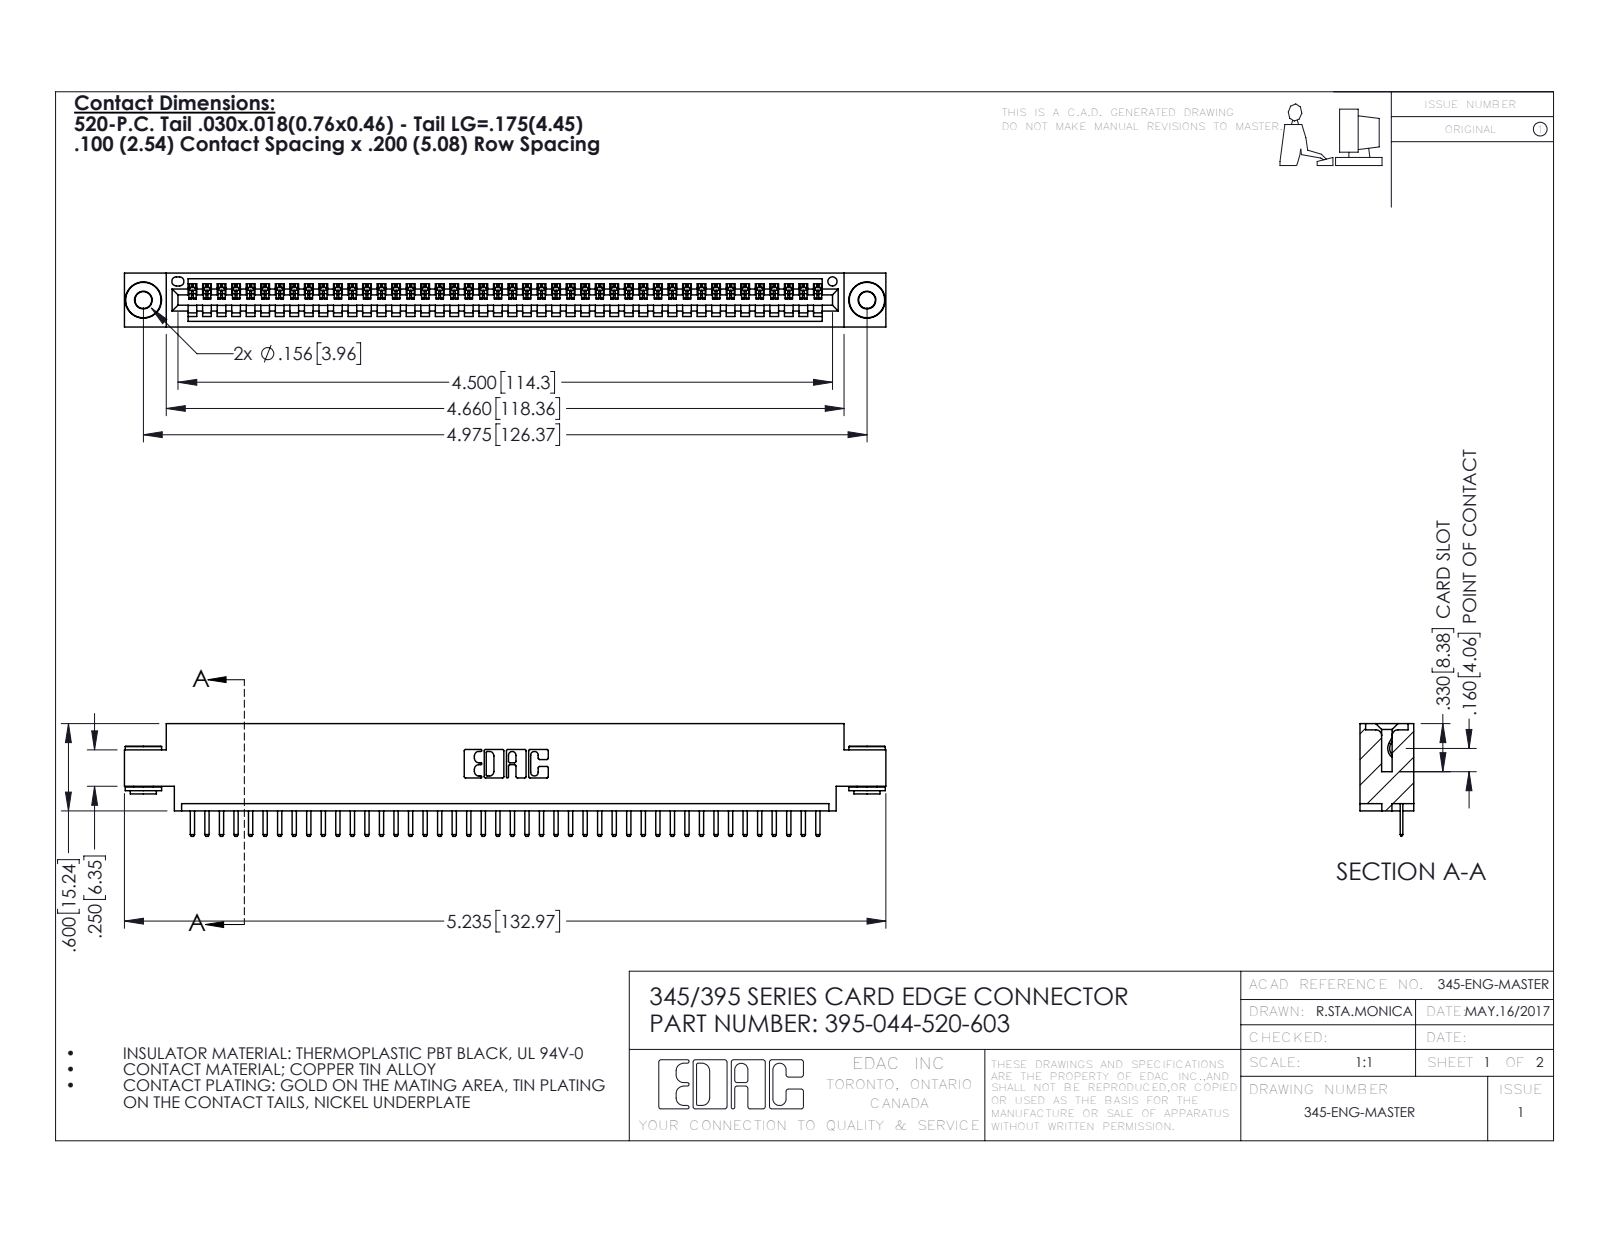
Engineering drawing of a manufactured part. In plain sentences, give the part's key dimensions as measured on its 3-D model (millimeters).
The part is named "345-292-001_345-293-120; 395-044-520-603; 345 Part_0.170 Offset - 0.156 Dia-TH; 345-250-002_345-250-002-102". Its 3-D file was written by "SolidWorks 2016 (CONFIG_CONTROL_DESIGN)". It is 47 solids with 2896 faces: 1942 planar, 946 cylindrical and 8 other. Overall it measures 133 by 19.7 by 9.4 millimeters. Its volume is 12 400 cubic millimeters and its surface area 16 460 square millimeters. Round holes: 2 of diameter 2.9, 2 of diameter 4, 1 of diameter 1.6. Round bosses or shafts: 2 of diameter 6.4, 2 of diameter 4.6, 2 of diameter 3.5. Partial cylindrical surfaces (rounded edges, fillets, slot ends): 90 of radius 0.3, 88 of radius 0.2, 22 of radius 0.3, 6 of radius 0.2, 6 of radius 0.8, 3 of radius 0.7, 2 of radius 0.8, 2 of radius 1. The main face-to-face distances are 1.8, 7.6, 9.4, 5.1, 2.5, 6.9, 0.6, 5.7, 4.4, 1.8. The hole center spacings are 6.9, 120.4, 126.4.
